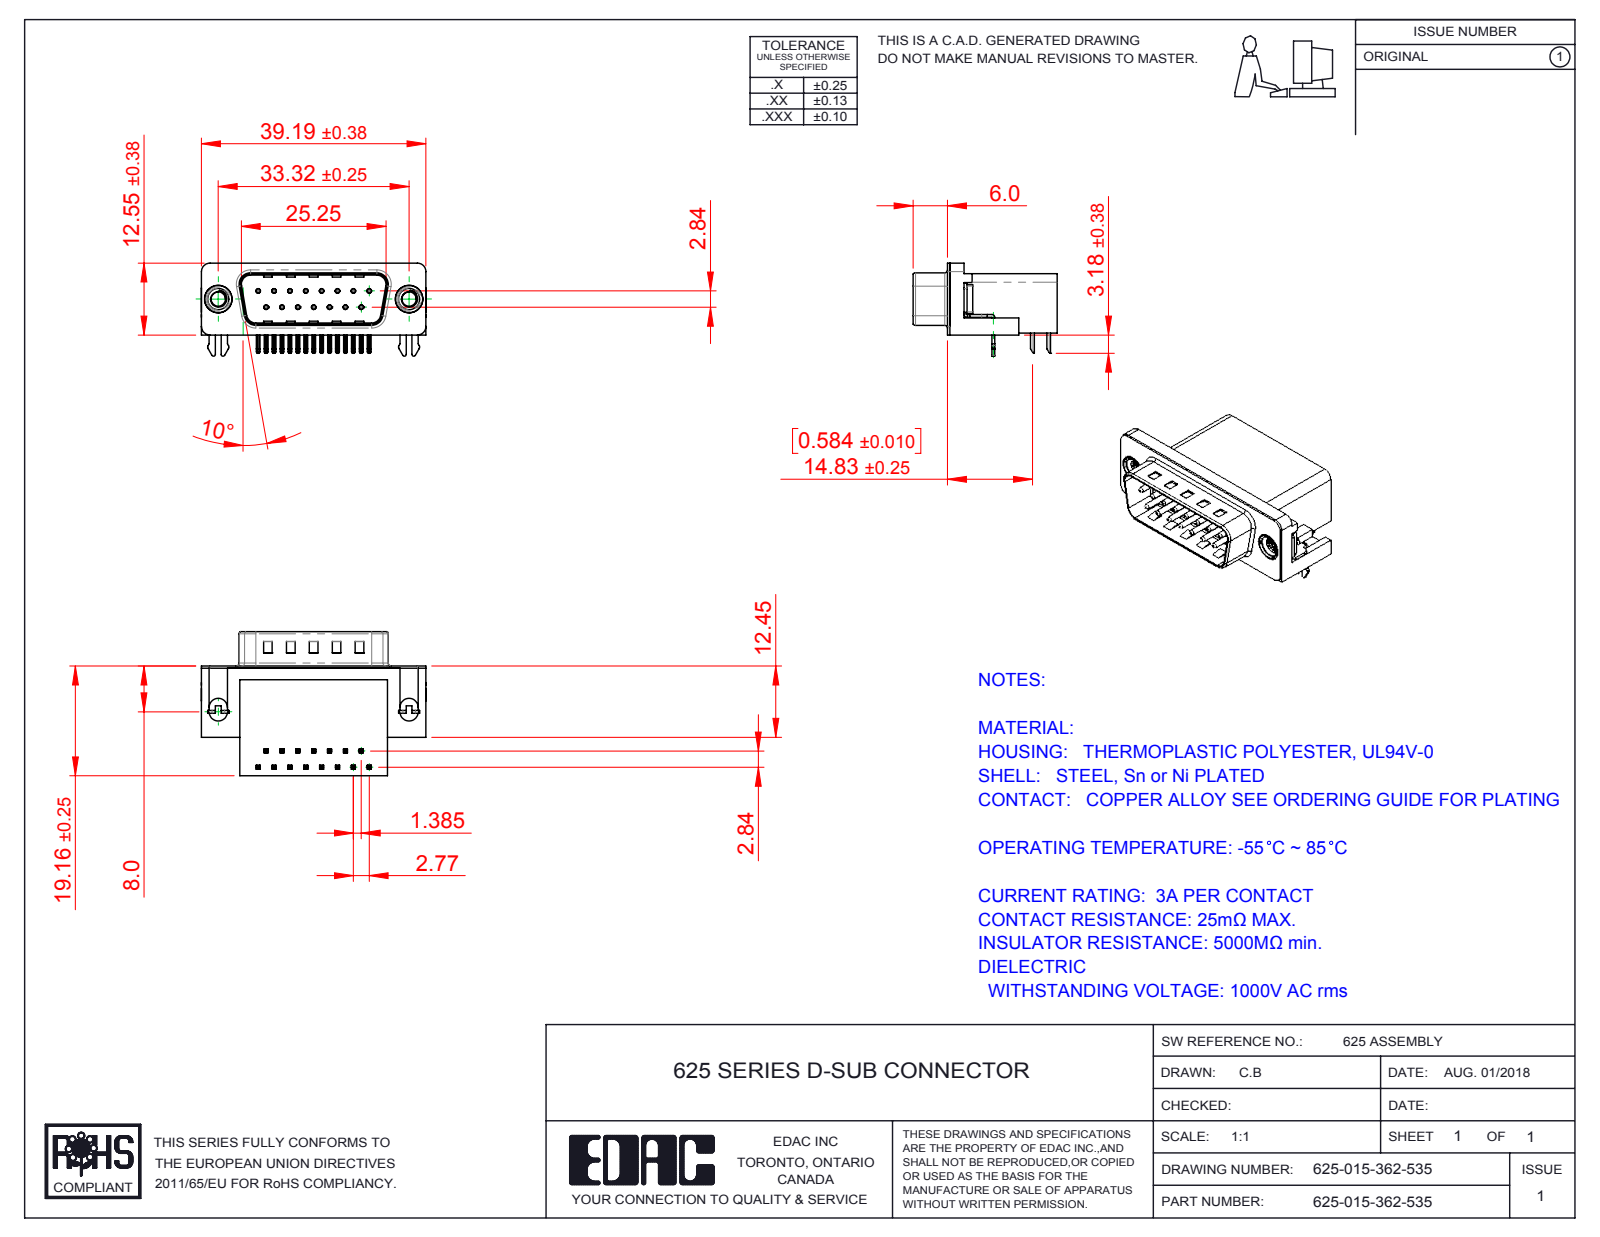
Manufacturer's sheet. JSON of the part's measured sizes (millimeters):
{"part_name": "625 Contact Bottom; 625-015-362-535; 625 2 Prong Board Lock; 625 Housing_15 Socket (+3 more)", "step_written_by": "SolidWorks 2016 (CONFIG_CONTROL_DESIGN)", "units": "millimeters", "bodies": {"solids": 21, "faces": 1519, "planar": 925, "cylindrical": 459, "other": 135}, "overall_size": [39.22, 25.16, 16.25], "volume_mm3": 6236, "surface_area_mm2": 6434, "round_holes": [[0.35, 15], [0.8, 15], [2.5, 2], [4, 2], [4.8, 2], [5, 2]], "round_bosses_or_shafts": [[0.75, 15], [4.9, 2], [4.75, 2], [3.9, 2]], "partial_cylinders_radius": [[0.25, 68], [0.12, 30], [1, 16], [0.5, 14], [1.6, 8], [1.5, 6], [0.32, 4], [0.9, 4]], "face_to_face_distances": [0.4, 10.35, 18.76, 2.1, 10.46, 19.16, 1.7, 10.86, 8.76, 16.26], "hole_center_spacings": [3.16, 2.77, 5.54, 8.31, 11.08, 5.03, 5.04, 7.48]}
